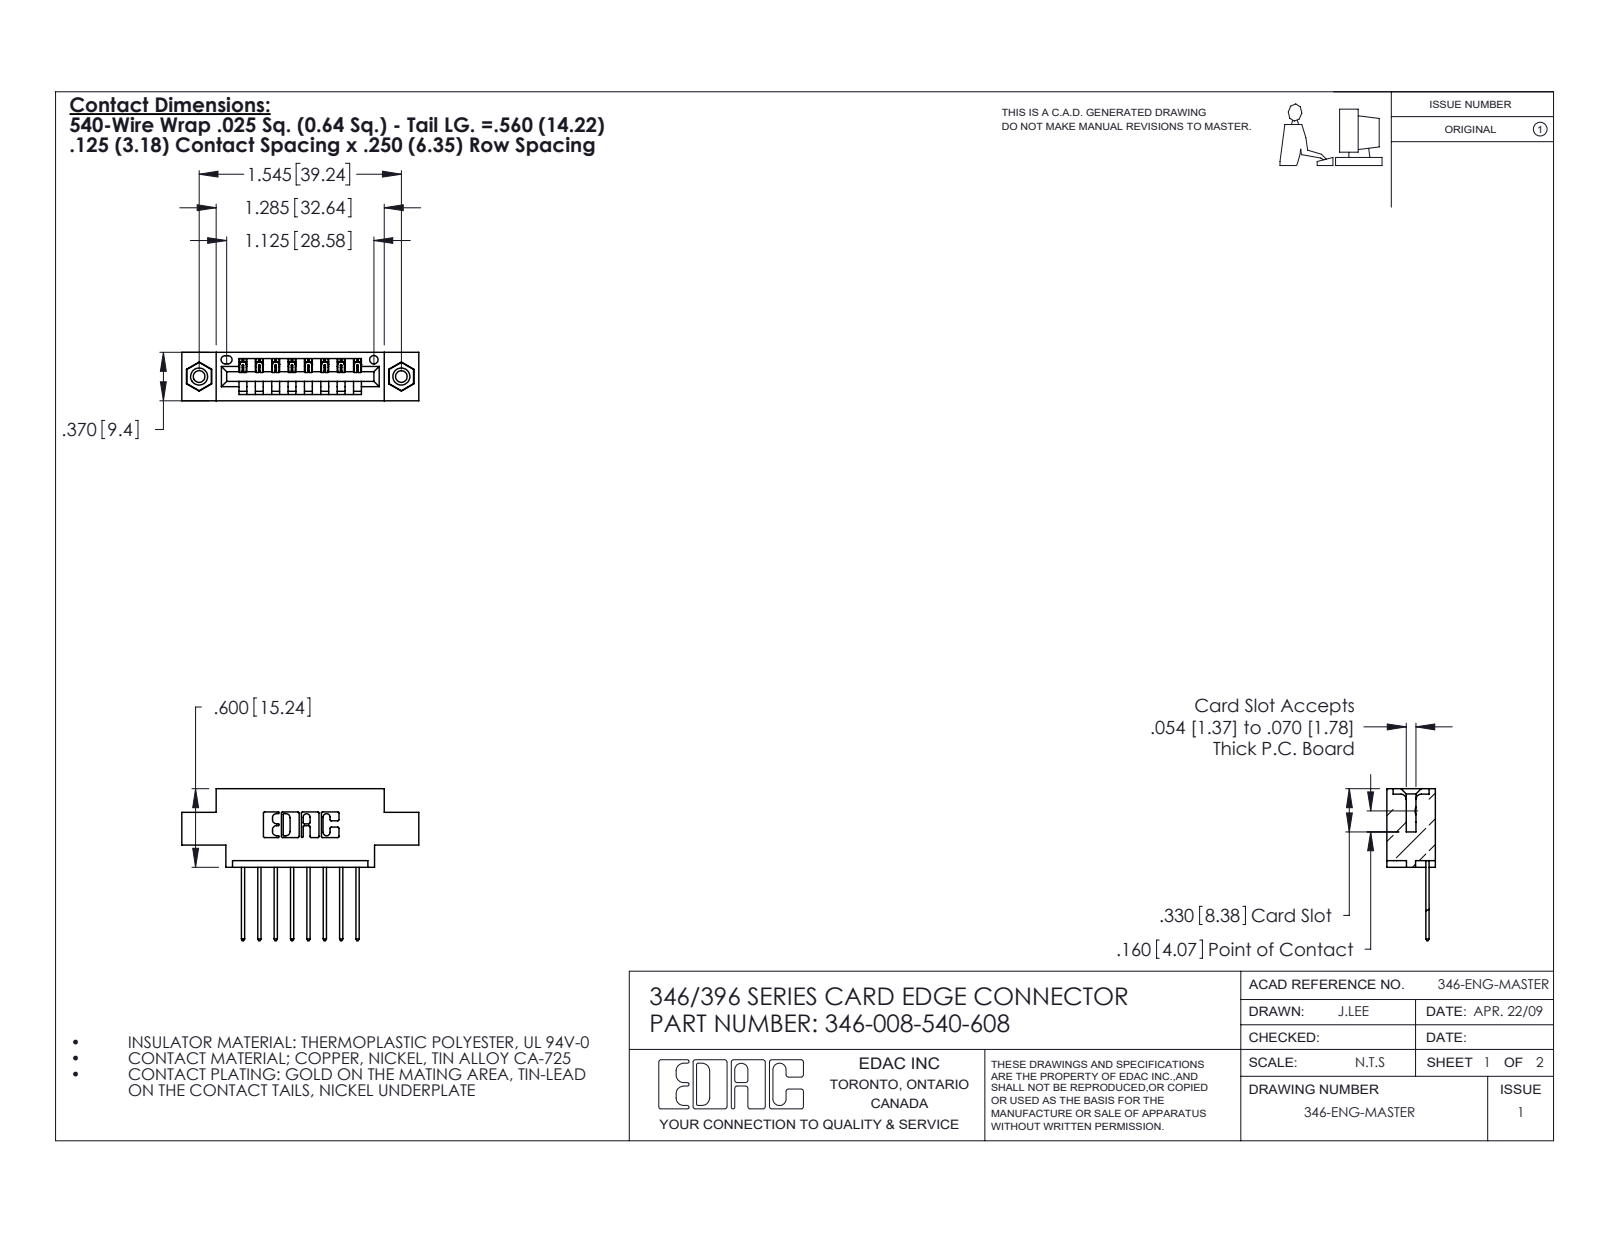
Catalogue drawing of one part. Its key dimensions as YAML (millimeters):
part_name: "346 Part_0.170 Offset - 0.156 Dia-TI; 345-250-001_345-250-003-102; 345-292-001_345-293-140; 346-008-540-608"
step_written_by: "SolidWorks 2020 (CONFIG_CONTROL_DESIGN)"
units: millimeters
bodies: {solids: 11, faces: 650, planar: 432, cylindrical: 202, other: 16}
overall_size: [46, 29.5, 9.4]
volume: 4010
surface_area: 4914
round_holes:
  - {diameter: 2.3, count: 2}
  - {diameter: 3.2, count: 2}
  - {diameter: 4, count: 2}
  - {diameter: 1.6, count: 1}
round_bosses_or_shafts:
  - {diameter: 3.9, count: 2}
partial_cylinders:
  - {radius: 0.3, count: 22}
  - {radius: 0.2, count: 16}
  - {radius: 0.3, count: 16}
  - {radius: 0.2, count: 6}
  - {radius: 0.8, count: 6}
  - {radius: 0.7, count: 3}
  - {radius: 0.8, count: 2}
  - {radius: 1, count: 2}
face_to_face_distances: [6.4, 9.4, 1.2, 8.2, 1.8, 7.6, 0.6, 5.6, 3.8, 2.5]
hole_center_spacings: [6.2, 34.1, 39.2]
